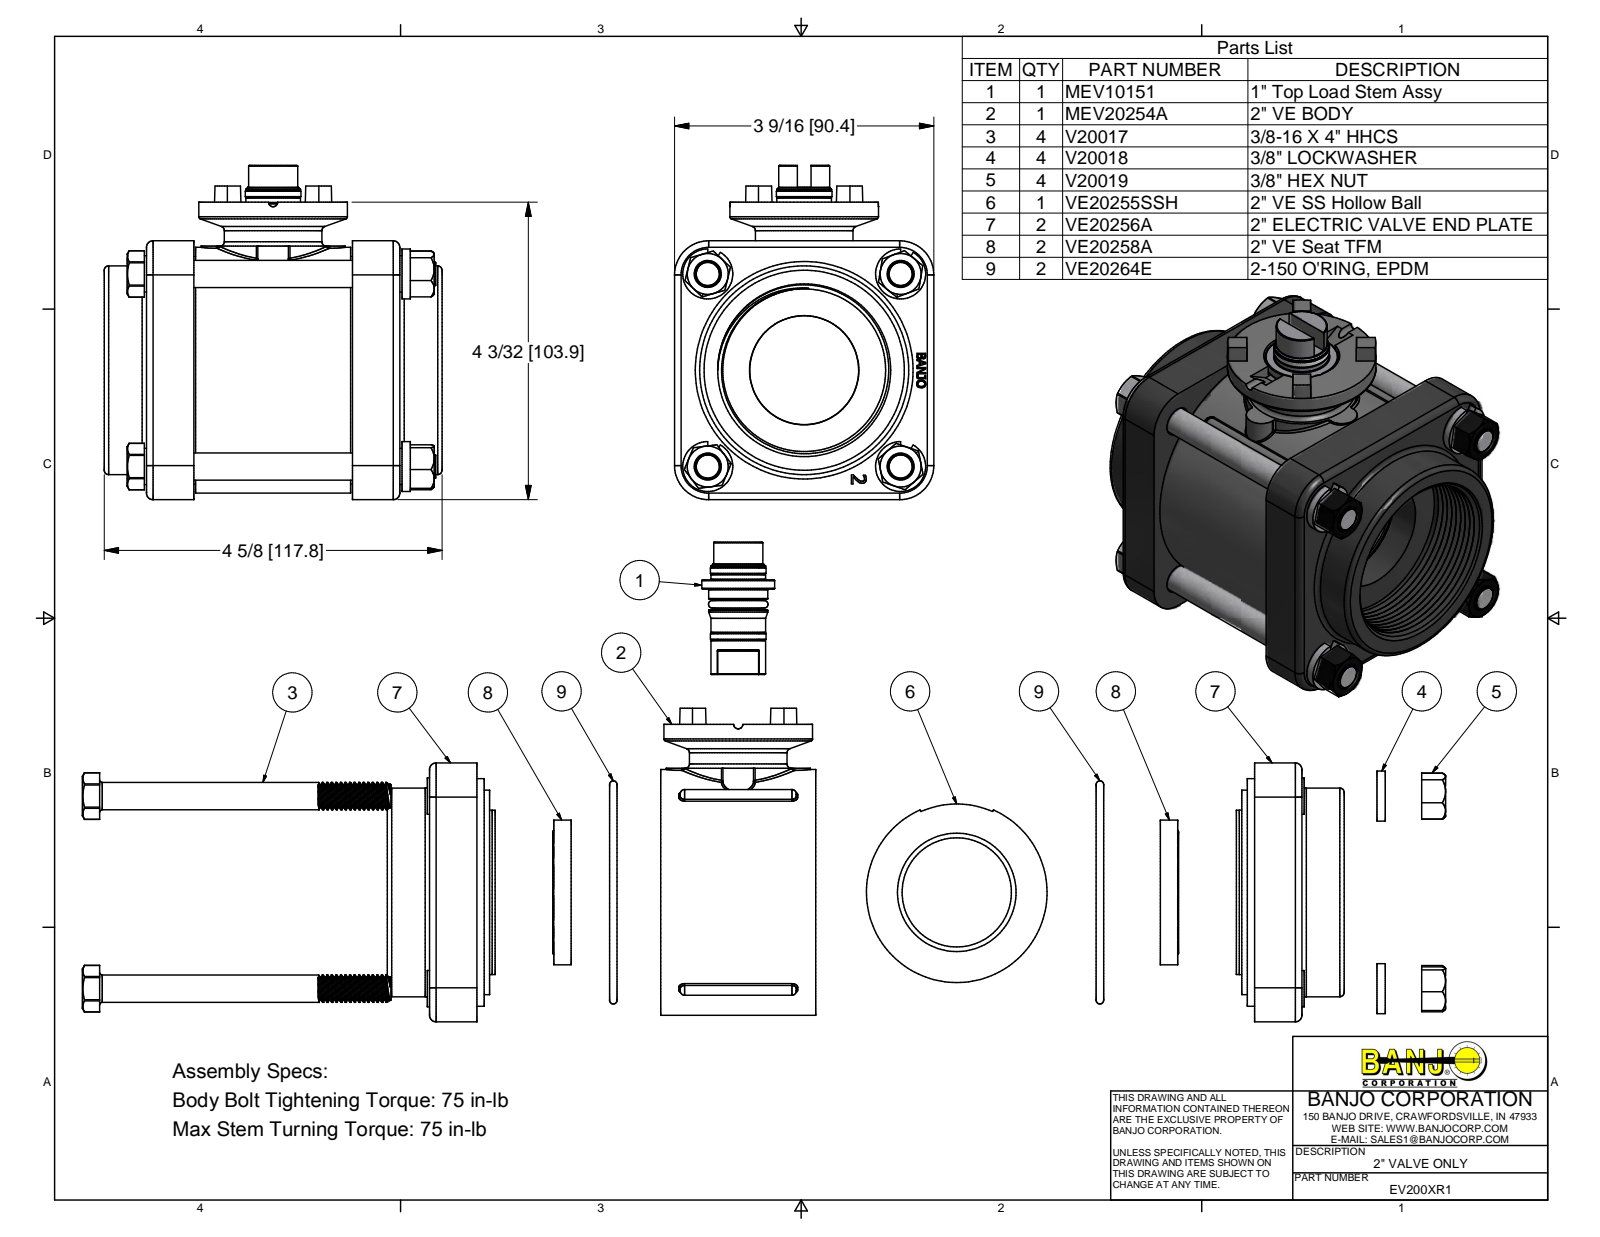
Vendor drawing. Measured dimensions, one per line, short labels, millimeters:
name: MEV20254AX; MEV20254A; VE20255SSH; MEV10151SS (+8 more)
written by: Autodesk Inventor 2014 (AUTOMOTIVE_DESIGN)
unit: mm
bodies: 26 solids, 1235 faces (346 planar, 367 cylindrical, 522 other)
size: 117.81 × 116.74 × 90.42
volume: 478 408 mm³; area: 168 001 mm²
holes: 4× ⌀7.81, 4× ⌀9.78, 4× ⌀10.31, 2× ⌀38.1, 1× ⌀16.38, 1× ⌀19.3, 1× ⌀20.78, 1× ⌀25.91, 1× ⌀26.42, 1× ⌀37.97, 1× ⌀50.67, 1× ⌀56.79
bosses: 60× ⌀8.24, 4× ⌀17.46, 4× ⌀12.7, 4× ⌀9.52, 1× ⌀85.85, 1× ⌀79.5, 1× ⌀72.9, 1× ⌀71.42
rounds: 12× R2.29, 8× R0.25, 8× R0.51, 8× R0.76, 8× R4.12, 4× R5.33, 4× R8.12, 4× R11.91
face distances: 16.51, 71.83, 4.44, 20.95, 67.39, 50.88, 90.42, 7.11, 81.23, 9.4
hole spacings: 47.56, 67.26, 95.12
